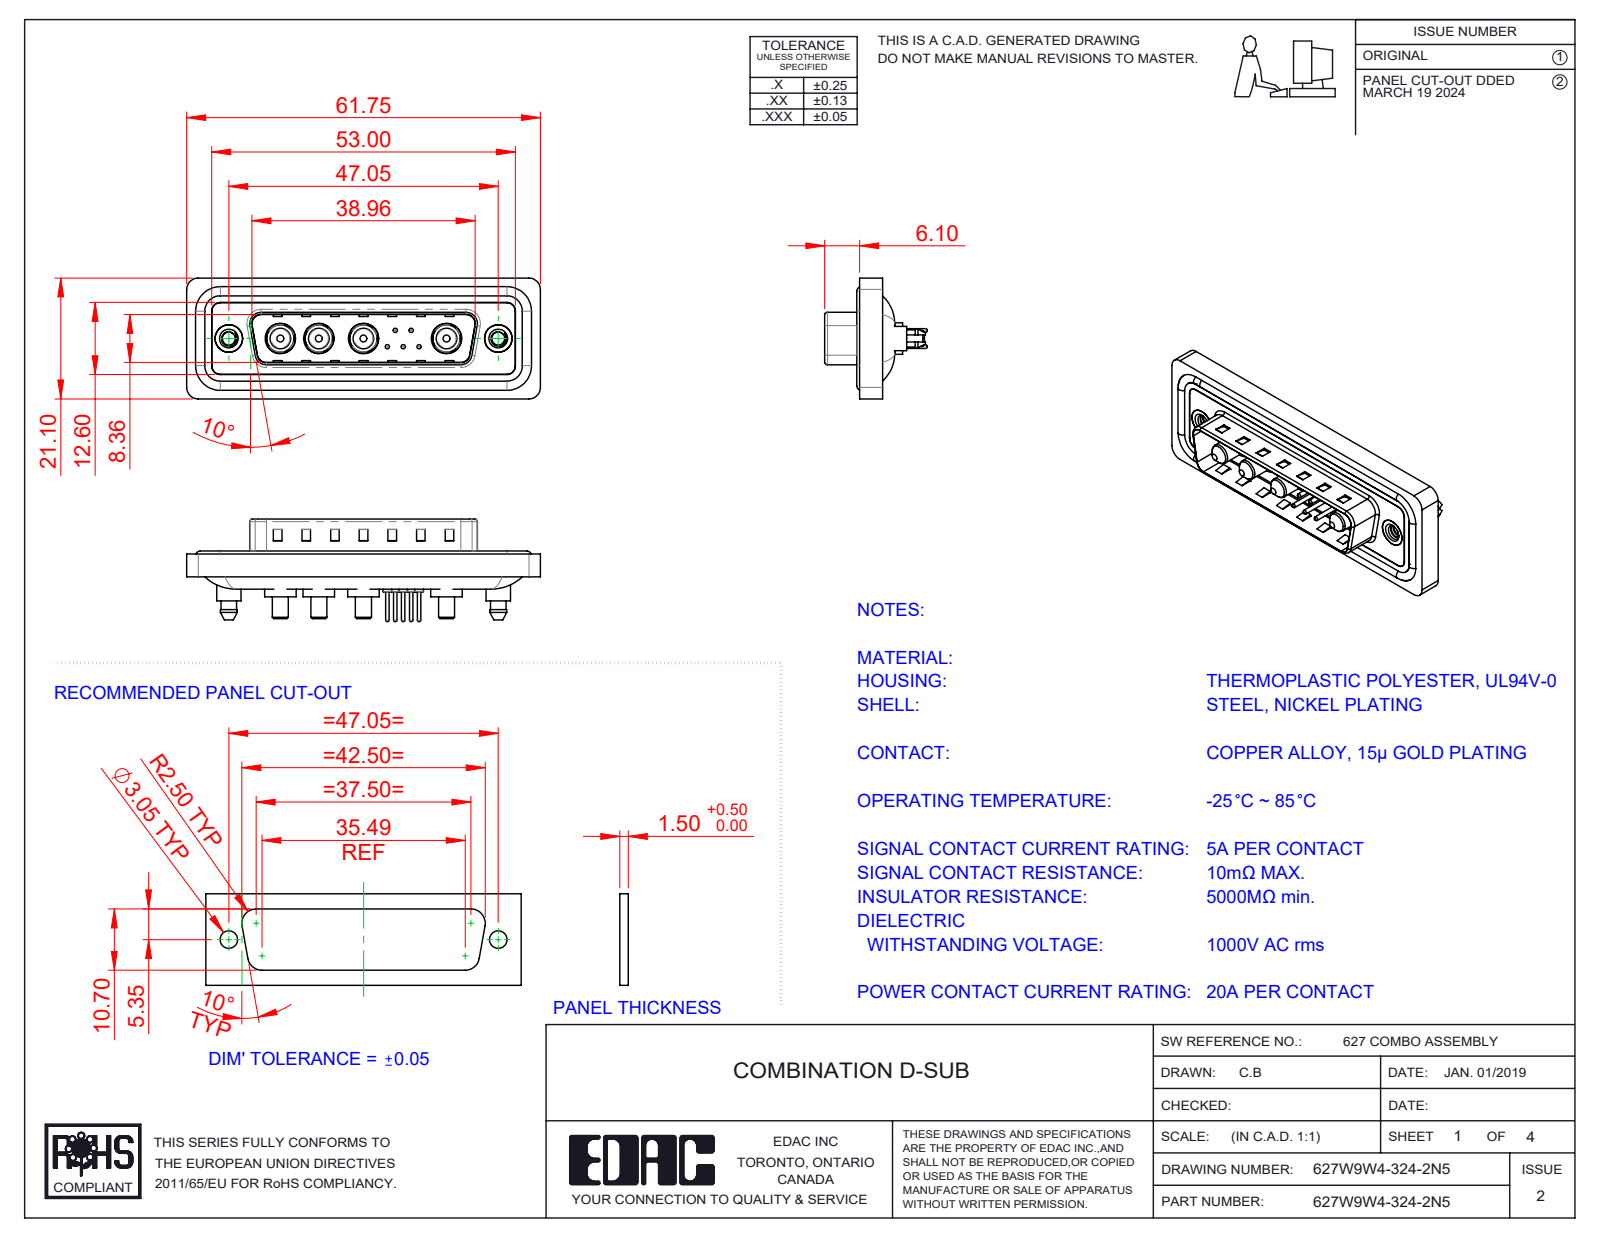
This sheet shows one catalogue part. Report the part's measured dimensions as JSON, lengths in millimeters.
{"part_name": "Power Pin_20A S; 627Combo Contact Row 1_24; 627Combo Housing_9W4; 627Combo Shell Front_25 Contacts (+5 more)", "step_written_by": "SolidWorks 2023 (CONFIG_CONTROL_DESIGN)", "units": "millimeters", "bodies": {"solids": 20, "faces": 874, "planar": 300, "cylindrical": 366, "other": 208}, "overall_size": [61.75, 21.1, 17.9], "volume_mm3": 7538, "surface_area_mm2": 12168, "round_holes": [[0.75, 5], [1.6, 5], [2, 5], [4.85, 4], [5.3, 4], [2.26, 2], [4, 2], [4.8, 2], [5, 2]], "round_bosses_or_shafts": [[1.5, 5], [0.6, 5], [5.5, 4], [5.2, 4], [4.75, 4], [3.75, 4], [3.6, 4], [2.8, 4]], "partial_cylinders_radius": [[1.5, 24], [2, 18], [1.6, 10], [0.5, 8], [0.25, 4], [0.6, 4], [0.65, 4], [0.9, 4]], "face_to_face_distances": [0.4, 1.5, 1.1, 0.5, 3.1, 1.6, 2.9, 0.82, 9.58, 5.65], "hole_center_spacings": [3.16, 2.77, 5.04, 14.51, 2.78, 4.4, 4.41, 5]}
